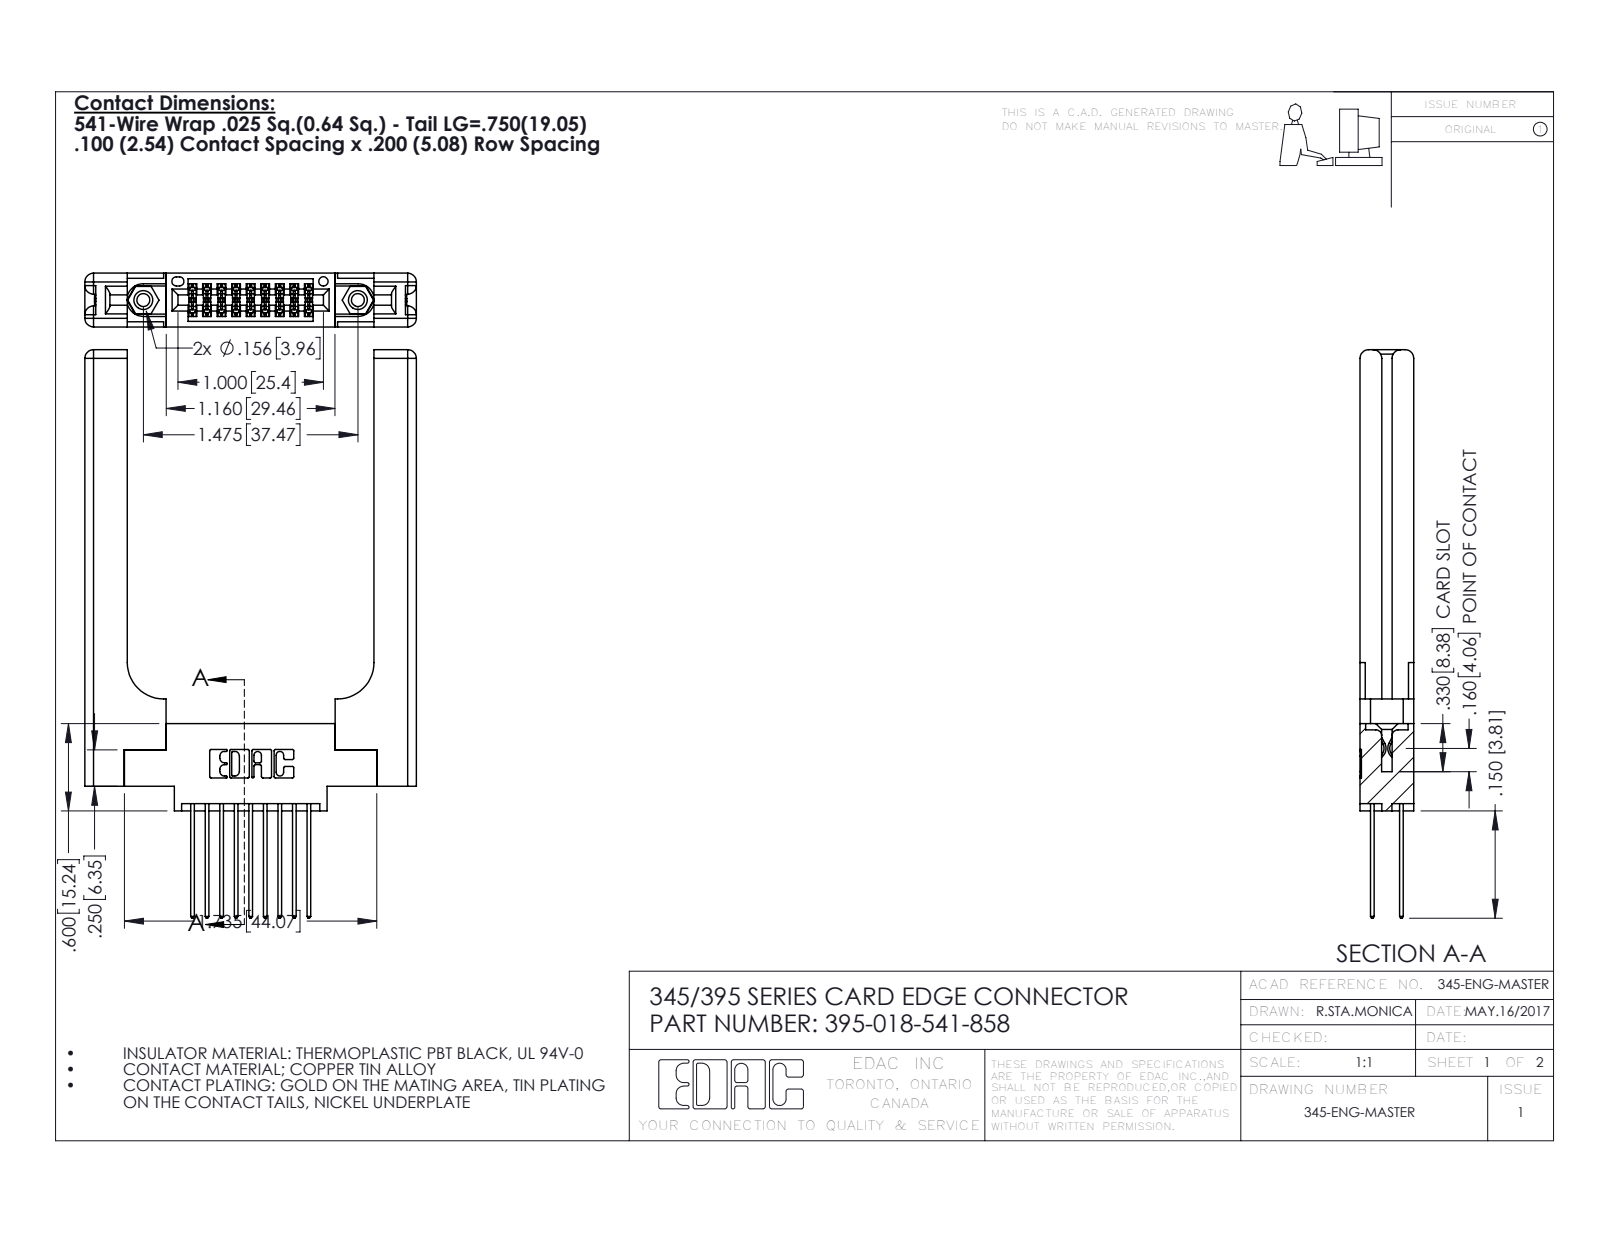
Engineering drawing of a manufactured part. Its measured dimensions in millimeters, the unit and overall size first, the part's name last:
Units: millimetres
Overall size (bounding box): 99.2 × 57.9 × 9.4
Round holes (diameter × count): ⌀2.3 ×2, ⌀3.2 ×2, ⌀4 ×2, ⌀1.6 ×1
Round bosses / shafts (diameter × count): ⌀3.9 ×2
Partial cylindrical surfaces — rounded edges, fillets, slot ends (radius × count): R0.2 ×27, R0.3 ×22, R0.3 ×18, R1.5 ×16, R0.2 ×6, R0.8 ×6, R0.7 ×3, R0.4 ×2
Main face-to-face distances: 9.4, 1.8, 7.6, 3.8, 2, 3.8, 5.6, 3.1, 2.5, 6.9
Hole centre spacings: 6.9, 31.6, 37.5
Volume: 13 800 mm³ · Surface area: 12 890 mm²
Bodies: 23 solids, 1286 faces (826 planar, 400 cylindrical, 60 other)
Part name (STEP PRODUCT): 345-220-058_345-220-058; 345-250-001_345-250-001-102; 345 Part_0.170 Offset - 0.156 Dia-TH; 345-292-001_345-293-141 (+1 more)
STEP written by: SolidWorks 2016 (CONFIG_CONTROL_DESIGN)
